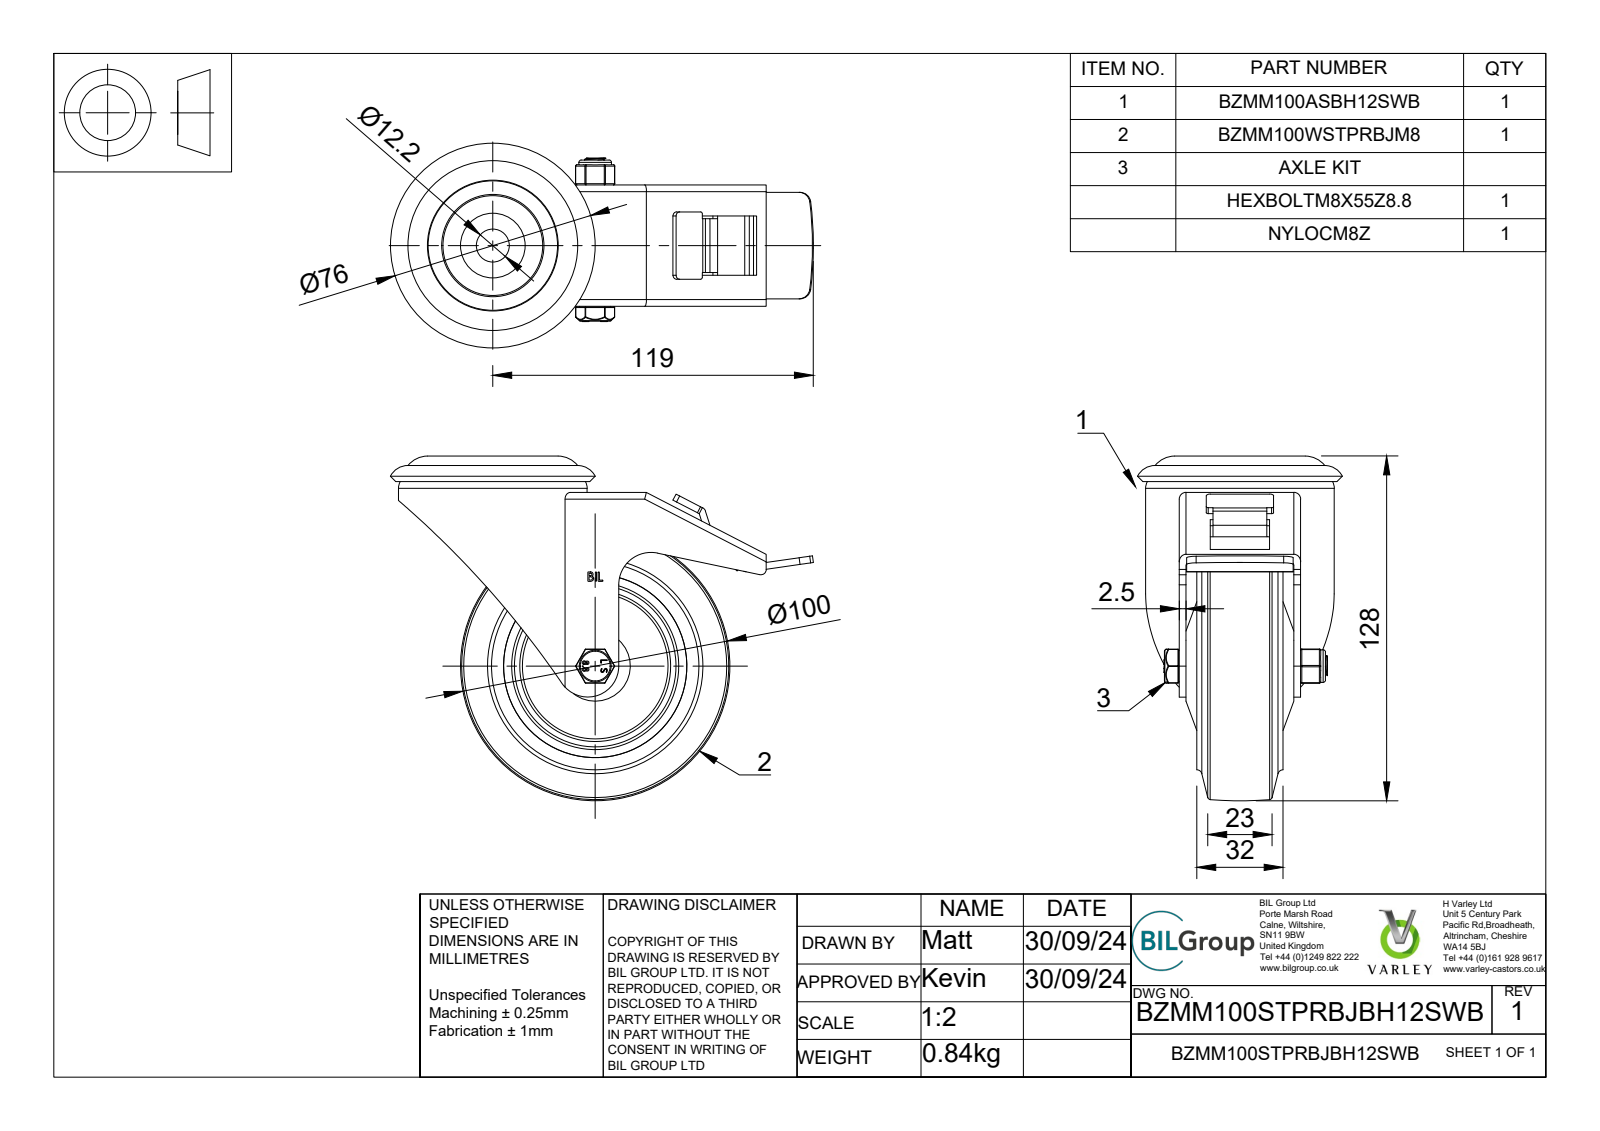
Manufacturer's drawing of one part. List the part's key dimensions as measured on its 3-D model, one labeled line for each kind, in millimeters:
Part name (STEP PRODUCT): BZMM100STPRBJBH12SWB v3; BZMM100ASBH12SWB v1; PRESSED STEEL, ZINC PLATED HEAD; PRESSED STEEL, ZINC PLATED FORKS (+8 more)
STEP written by: Autodesk Translation Framework v13.20.0.188 (AUTOMOTIVE_DESIGN)
Units: millimetres
Bodies: 24 solids, 953 faces (421 planar, 252 cylindrical, 280 other)
Overall size (bounding box): 157 × 128 × 76
Volume: 253 103 mm³ · Surface area: 138 878 mm²
Round holes (diameter × count): ⌀0.66 ×2, ⌀8 ×1, ⌀8.2 ×1, ⌀8.6 ×1, ⌀11.5 ×1, ⌀12.2 ×1, ⌀15 ×1, ⌀20 ×1, ⌀22.5 ×1, ⌀30 ×1, ⌀31 ×1, ⌀32 ×1
Round bosses / shafts (diameter × count): ⌀70 ×1, ⌀56 ×1, ⌀49.5 ×1, ⌀44 ×1, ⌀38 ×1, ⌀35 ×1, ⌀30.5 ×1, ⌀24 ×1
Partial cylindrical surfaces — rounded edges, fillets, slot ends (radius × count): R0.75 ×50, R0.5 ×18, R0.25 ×12, R1.25 ×10, R0.33 ×4, R0.64 ×4, R2.5 ×4, R2 ×3
Main face-to-face distances: 2.5, 6.5, 4, 13.5, 42.5, 17.5, 38.5, 36, 25, 20
Hole centre spacings: 3.22, 2.49
